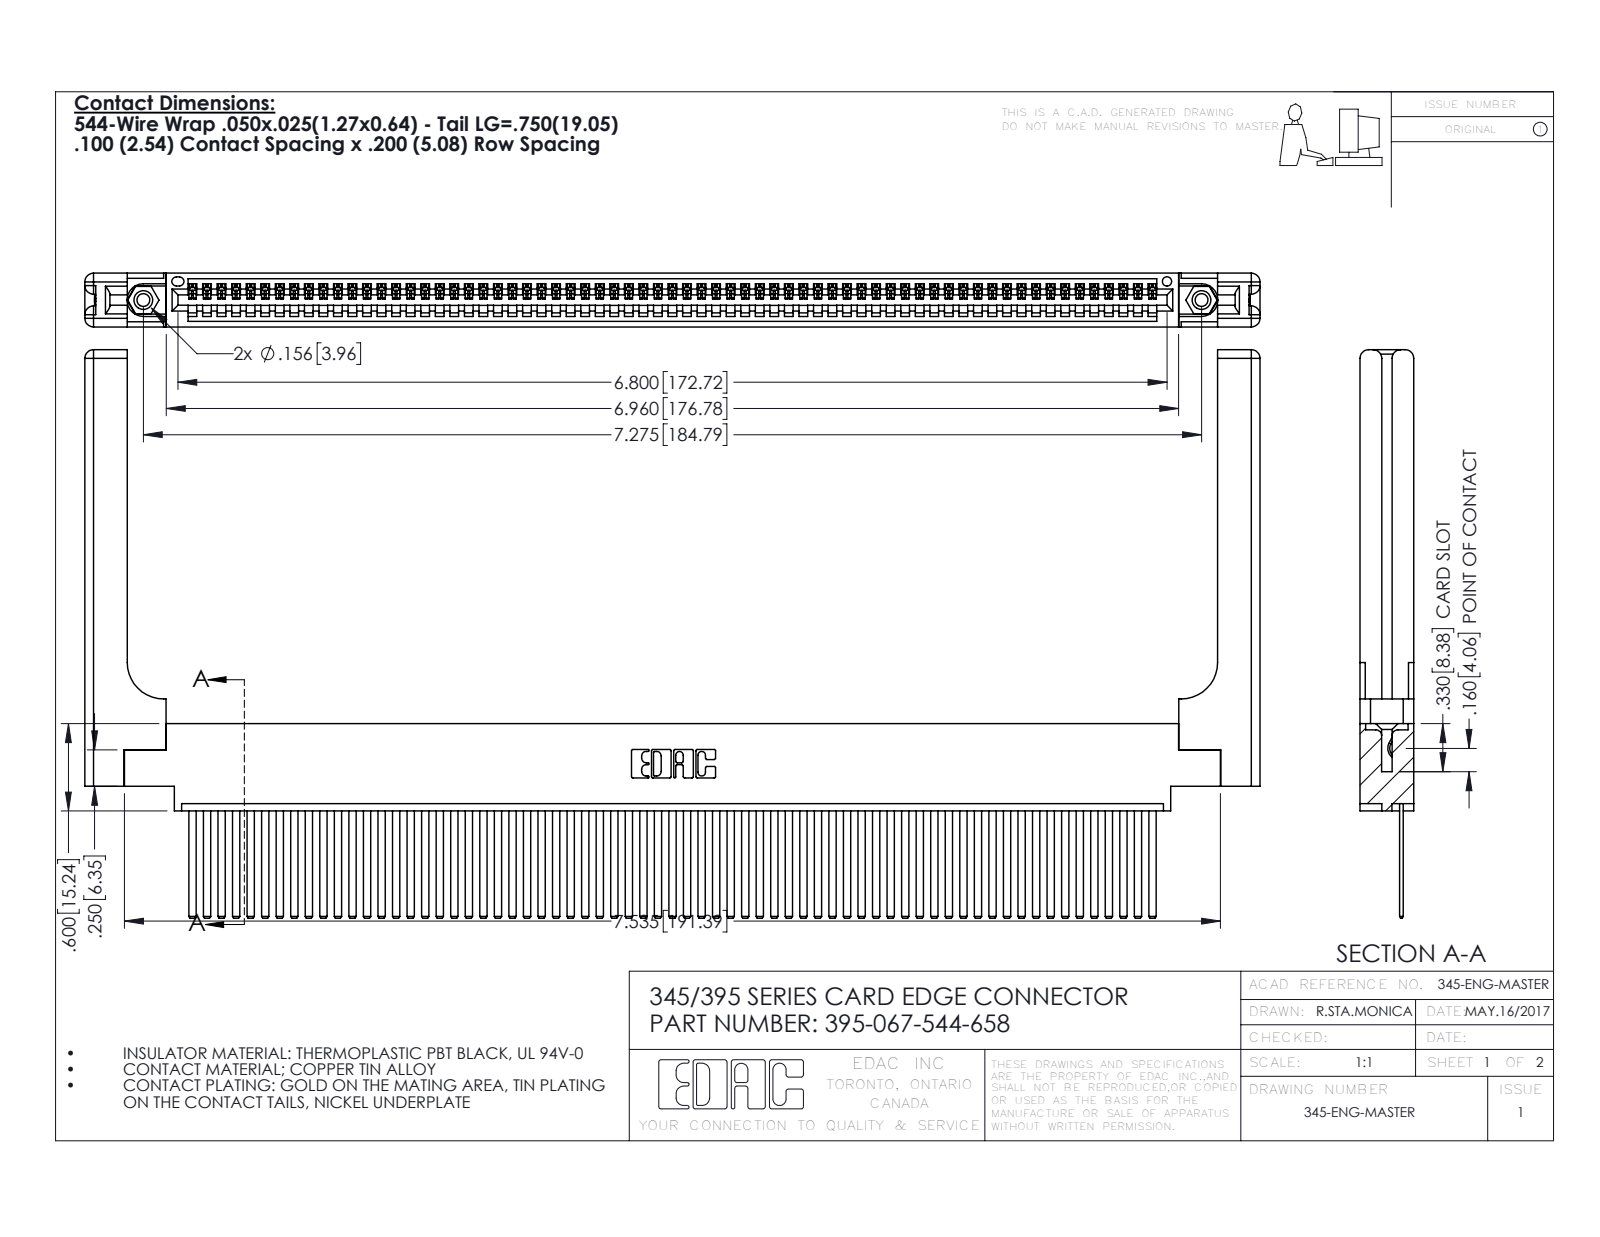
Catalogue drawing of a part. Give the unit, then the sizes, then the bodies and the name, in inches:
Units: inches
Overall size (bounding box): 8.079 × 3.907 × 0.37
Round holes (diameter × count): ⌀0.089 ×2, ⌀0.125 ×2, ⌀0.156 ×2, ⌀0.064 ×1
Round bosses / shafts (diameter × count): ⌀0.155 ×2
Partial cylindrical surfaces — rounded edges, fillets, slot ends (radius × count): R0.006 ×134, R0.01 ×22, R0.06 ×16, R0.007 ×6, R0.031 ×6, R0.026 ×3, R0.03 ×2, R0.031 ×2
Main face-to-face distances: 0.072, 0.298, 0.37, 0.098, 0.272, 0.025, 0.2, 0.225, 0.148, 0.15
Hole centre spacings: 0.27, 7.039, 7.275
Volume: 1.761 in³ · Surface area: 54.49 in²
Bodies: 72 solids, 3870 faces (2644 planar, 1166 cylindrical, 60 other)
Part name (STEP PRODUCT): 345-250-001_345-250-001-102; 345-220-058_345-220-058; 395-067-544-658; 345-292-001_345-293-144 (+1 more)
STEP written by: SolidWorks 2016 (CONFIG_CONTROL_DESIGN)
